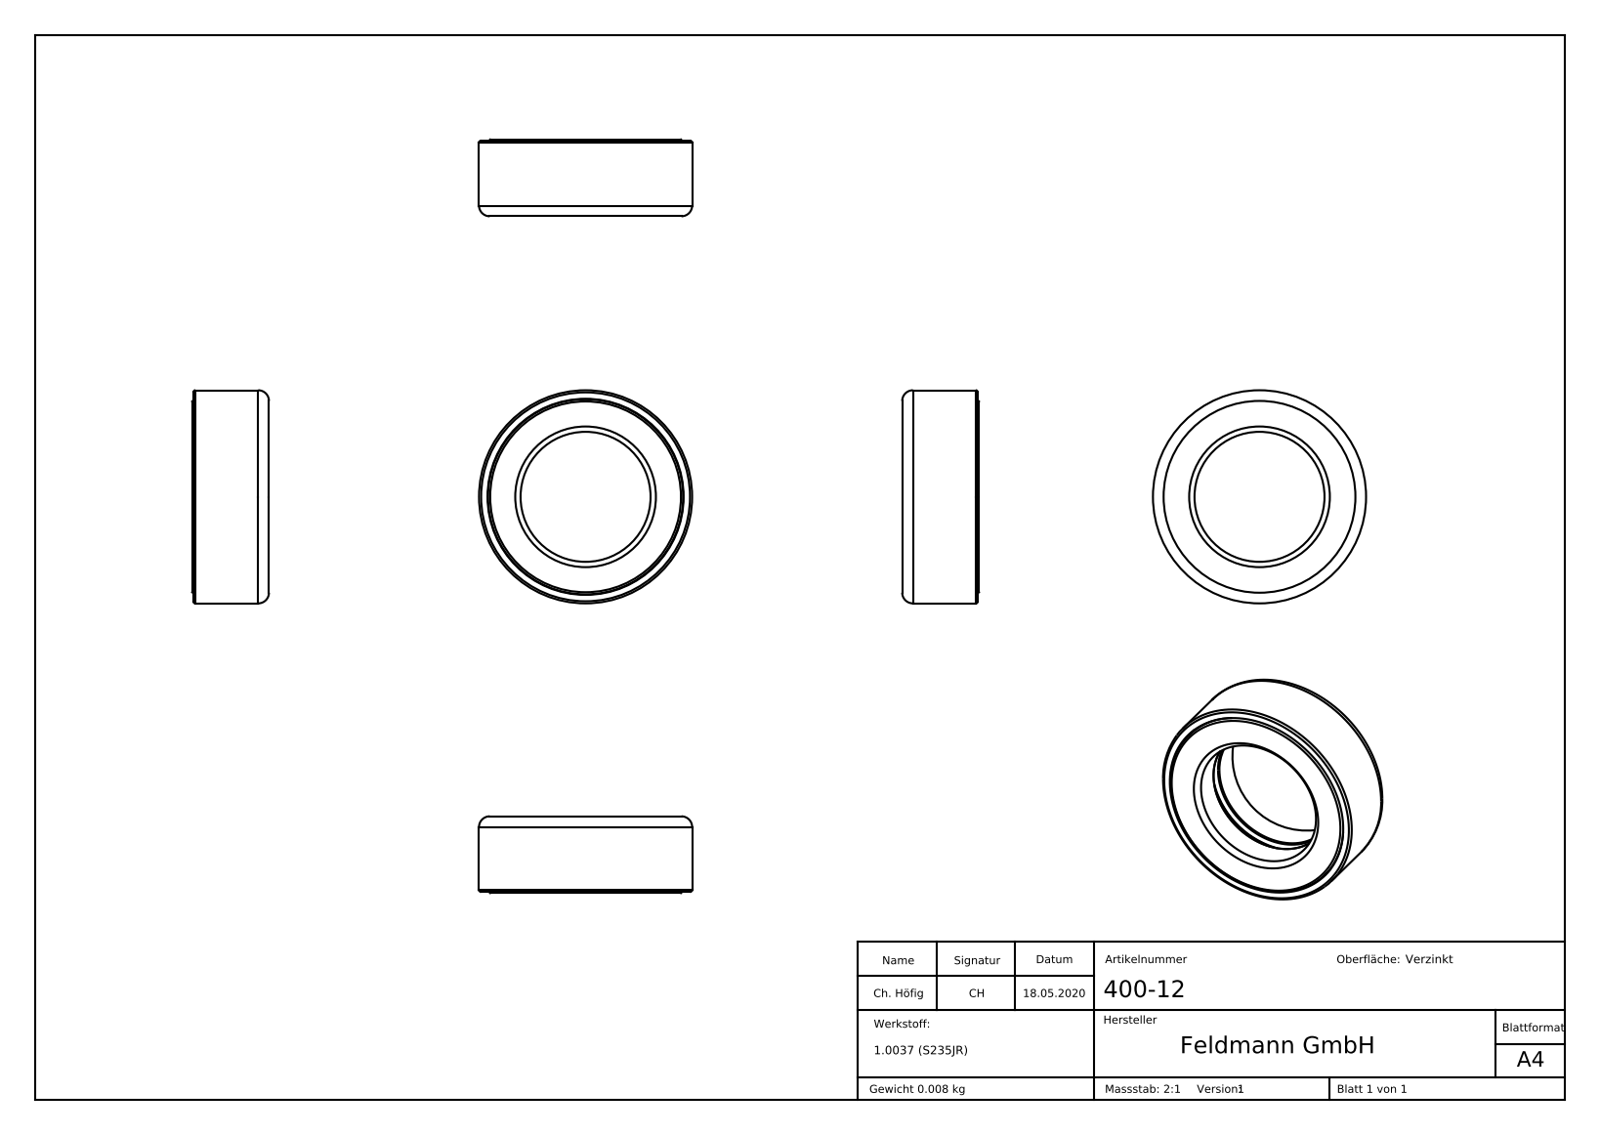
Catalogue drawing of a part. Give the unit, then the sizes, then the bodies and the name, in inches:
Units: inches
Overall size (bounding box): 0.787 × 0.787 × 0.283
Round holes (diameter × count): ⌀0.48 ×1, ⌀0.657 ×1, ⌀0.724 ×1
Round bosses / shafts (diameter × count): ⌀0.787 ×1, ⌀0.72 ×1, ⌀0.543 ×1
Main face-to-face distances: 0.031, 0.252, 0.283, 0.22, 0.122, 0.161, 0.091, 0.13, 0.033, 0.219
Volume: 0.061 in³ · Surface area: 4.216 in²
Bodies: 26 solids, 49 faces (8 planar, 8 cylindrical, 33 other)
Part name (STEP PRODUCT): 400-12
STEP written by: SolidWorks 2015 (CONFIG_CONTROL_DESIGN)
